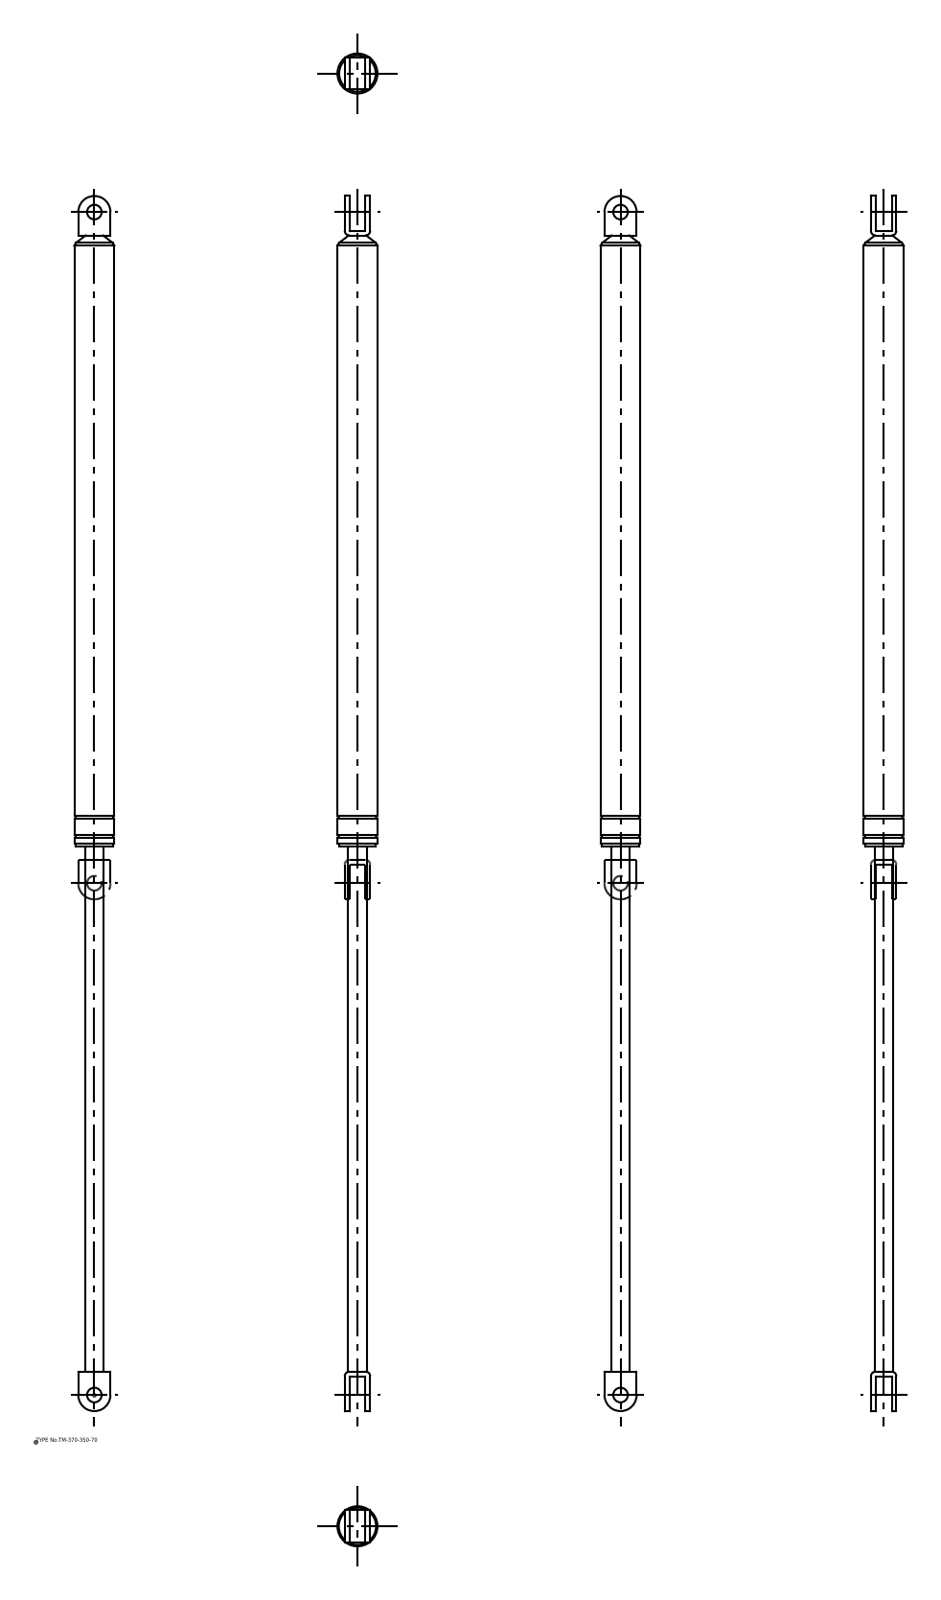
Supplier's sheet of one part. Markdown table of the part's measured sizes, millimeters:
| quantity | value |
| --- | --- |
| part name | TM_370_350_70; TM_370_350_70_div |
| STEP written by | spGate 16.7.1 (AUTOMOTIVE_DESIGN) |
| units | millimeters |
| bodies | 2 solids, 64 faces (22 planar, 32 cylindrical, 10 other) |
| overall size | 831 × 28.2 × 28.2 |
| volume | 296 250 mm³ |
| surface area | 56 860 mm² |
| round holes (diameter × count) | 10 × 2 |
| round bosses / shafts (diameter × count) | 28.2 × 1, 27.4 × 1, 25.5 × 1, 12.5 × 1 |
| partial cylindrical surfaces (radius × count) | 3.2 × 4, 11 × 2 |
| main face-to-face distances | 3.2, 14.2, 17.4, 11, 22, 780.2, 362.2, 783.4, 421.2, 418 |
| hole center spacings | 809 |
